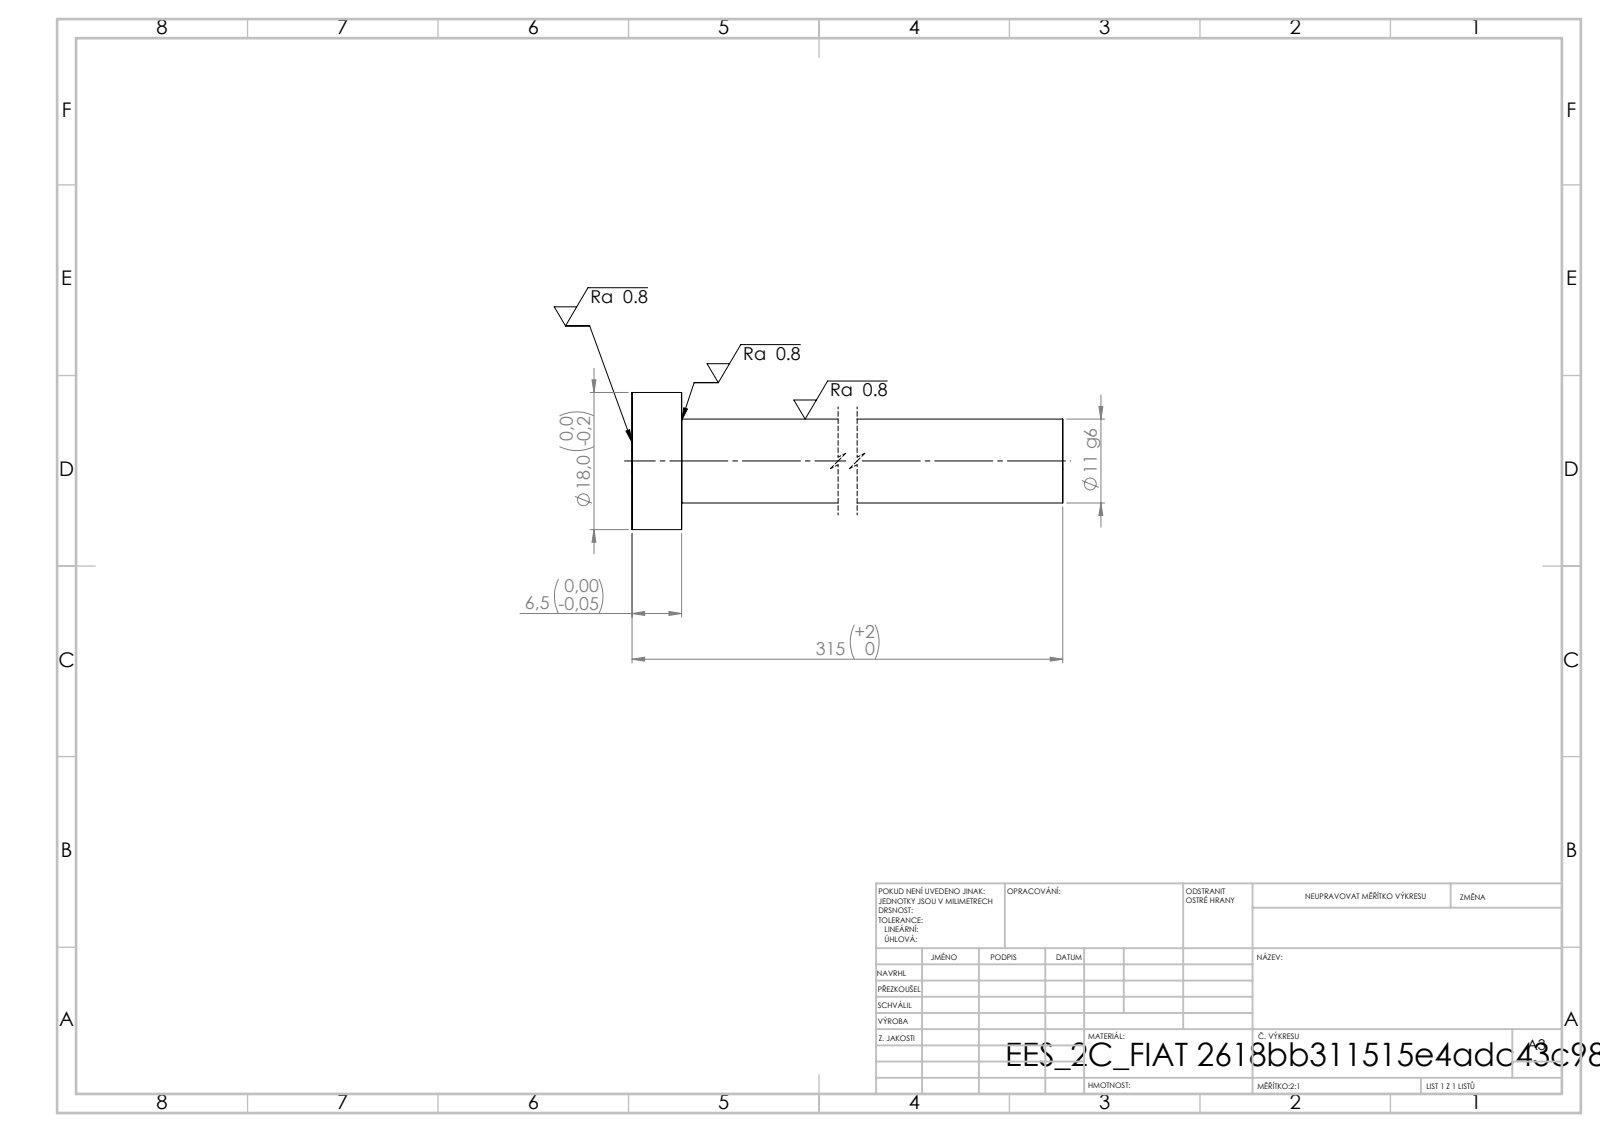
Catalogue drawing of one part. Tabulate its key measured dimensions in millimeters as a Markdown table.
| quantity | value |
| --- | --- |
| STEP written by | SolidWorks 2019 (CONFIG_CONTROL_DESIGN) |
| units | millimeters |
| bodies | 1 solid, 7 faces (3 planar, 4 cylindrical, 0 other) |
| overall size | 315 × 18 × 18 |
| volume | 30 972 mm³ |
| surface area | 11 538 mm² |
| round bosses / shafts (diameter × count) | 18 × 1, 11 × 1 |
| main face-to-face distances | 6.5, 315, 308.5 |
